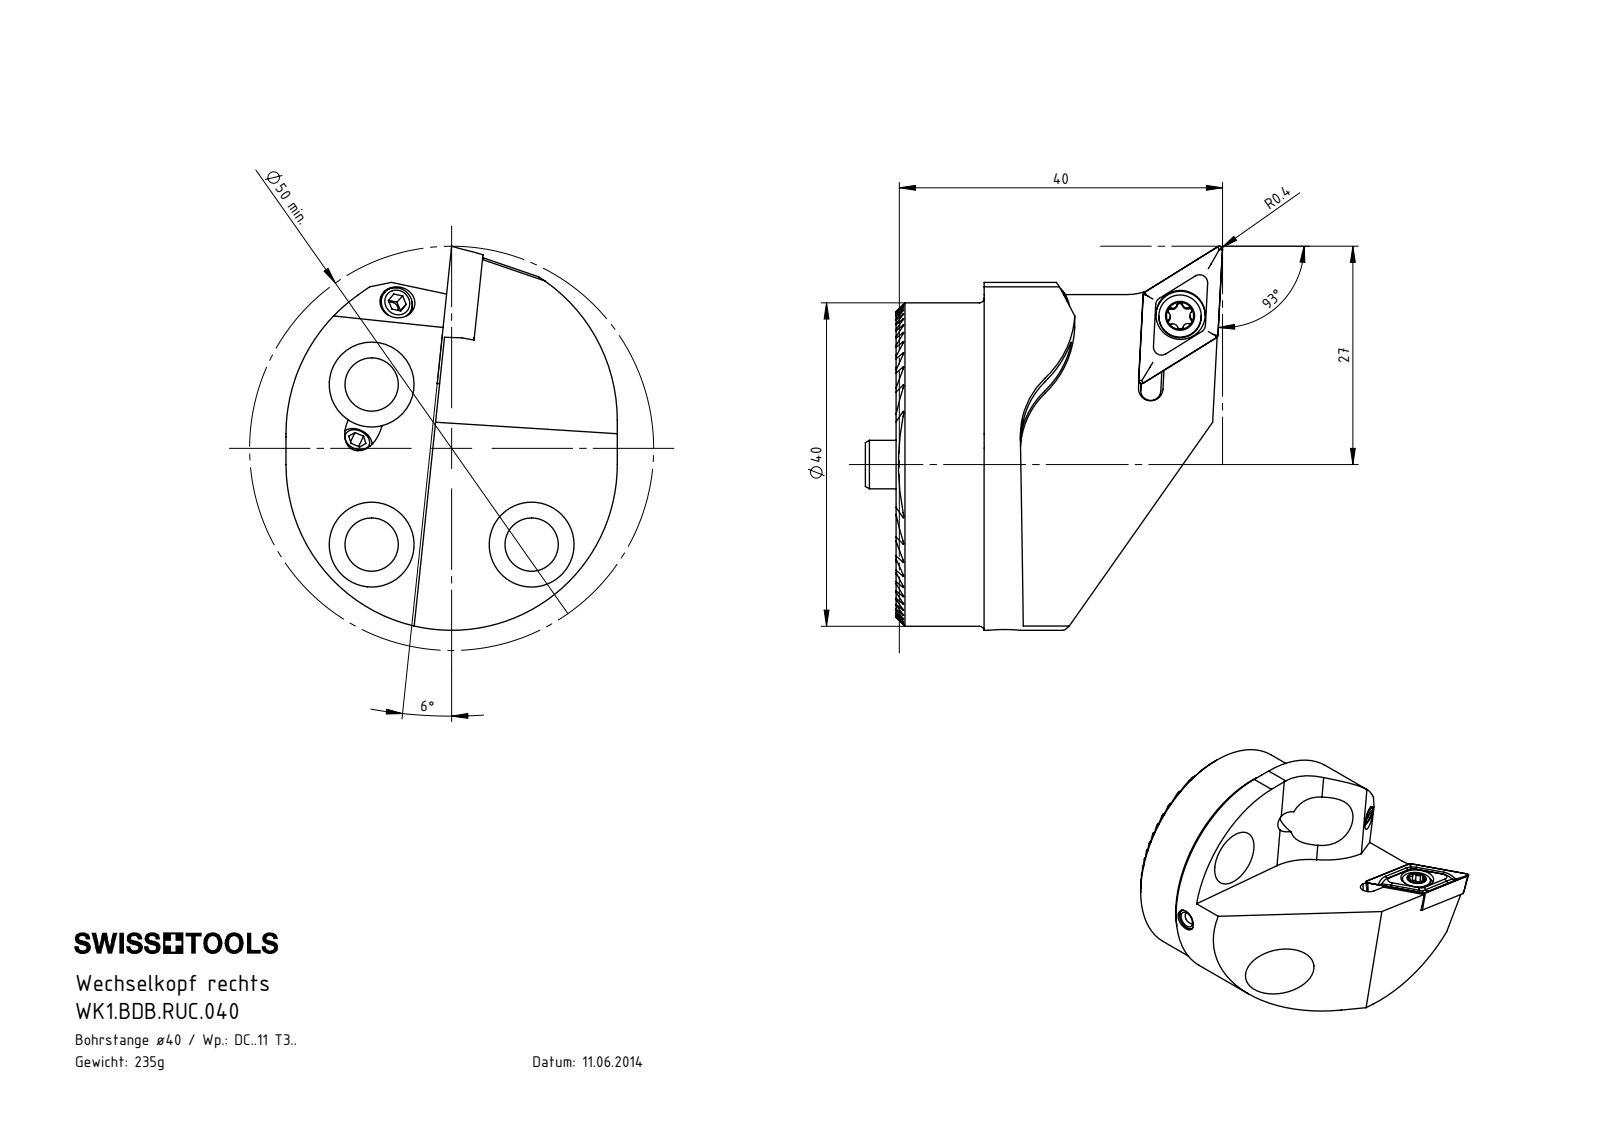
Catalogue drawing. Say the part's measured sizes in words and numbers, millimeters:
The part is named "DCMT11T304; WKX-ER1.004.005_A_PreviewCfg; WCB-ER2.001.009_A; KVT_MB_600_040 (+3 more)". Its 3-D file was written by "SolidWorks 2017 (AUTOMOTIVE_DESIGN)". It is 12 solids with 599 faces: 222 planar, 206 cylindrical and 171 other. Overall it measures 47.51 by 44.2 by 41 millimeters. Its volume is 29 719 cubic millimeters and its surface area 12 117 square millimeters. Round holes: 6 of diameter 3.3, 3 of diameter 3, 3 of diameter 4.2, 3 of diameter 6.6, 3 of diameter 10.5, 2 of diameter 1.7, 2 of diameter 4, 1 of diameter 4.4, 1 of diameter 6.1, 1 of diameter 12. Round bosses or shafts: 6 of diameter 4, 1 of diameter 40, 1 of diameter 6, 1 of diameter 5.25. Partial cylindrical surfaces (rounded edges, fillets, slot ends): 26 of radius 0.12, 6 of radius 0.34, 6 of radius 0.59, 2 of radius 21, 1 of radius 1.25, 1 of radius 7, 1 of radius 10, 1 of radius 12. The main face-to-face distances are 1.3, 2.6, 3.9, 12.99, 5.2, 11.69, 9.09, 10.39, 7.79, 6.5. The hole center spacings are 14, 19.8, 28.
